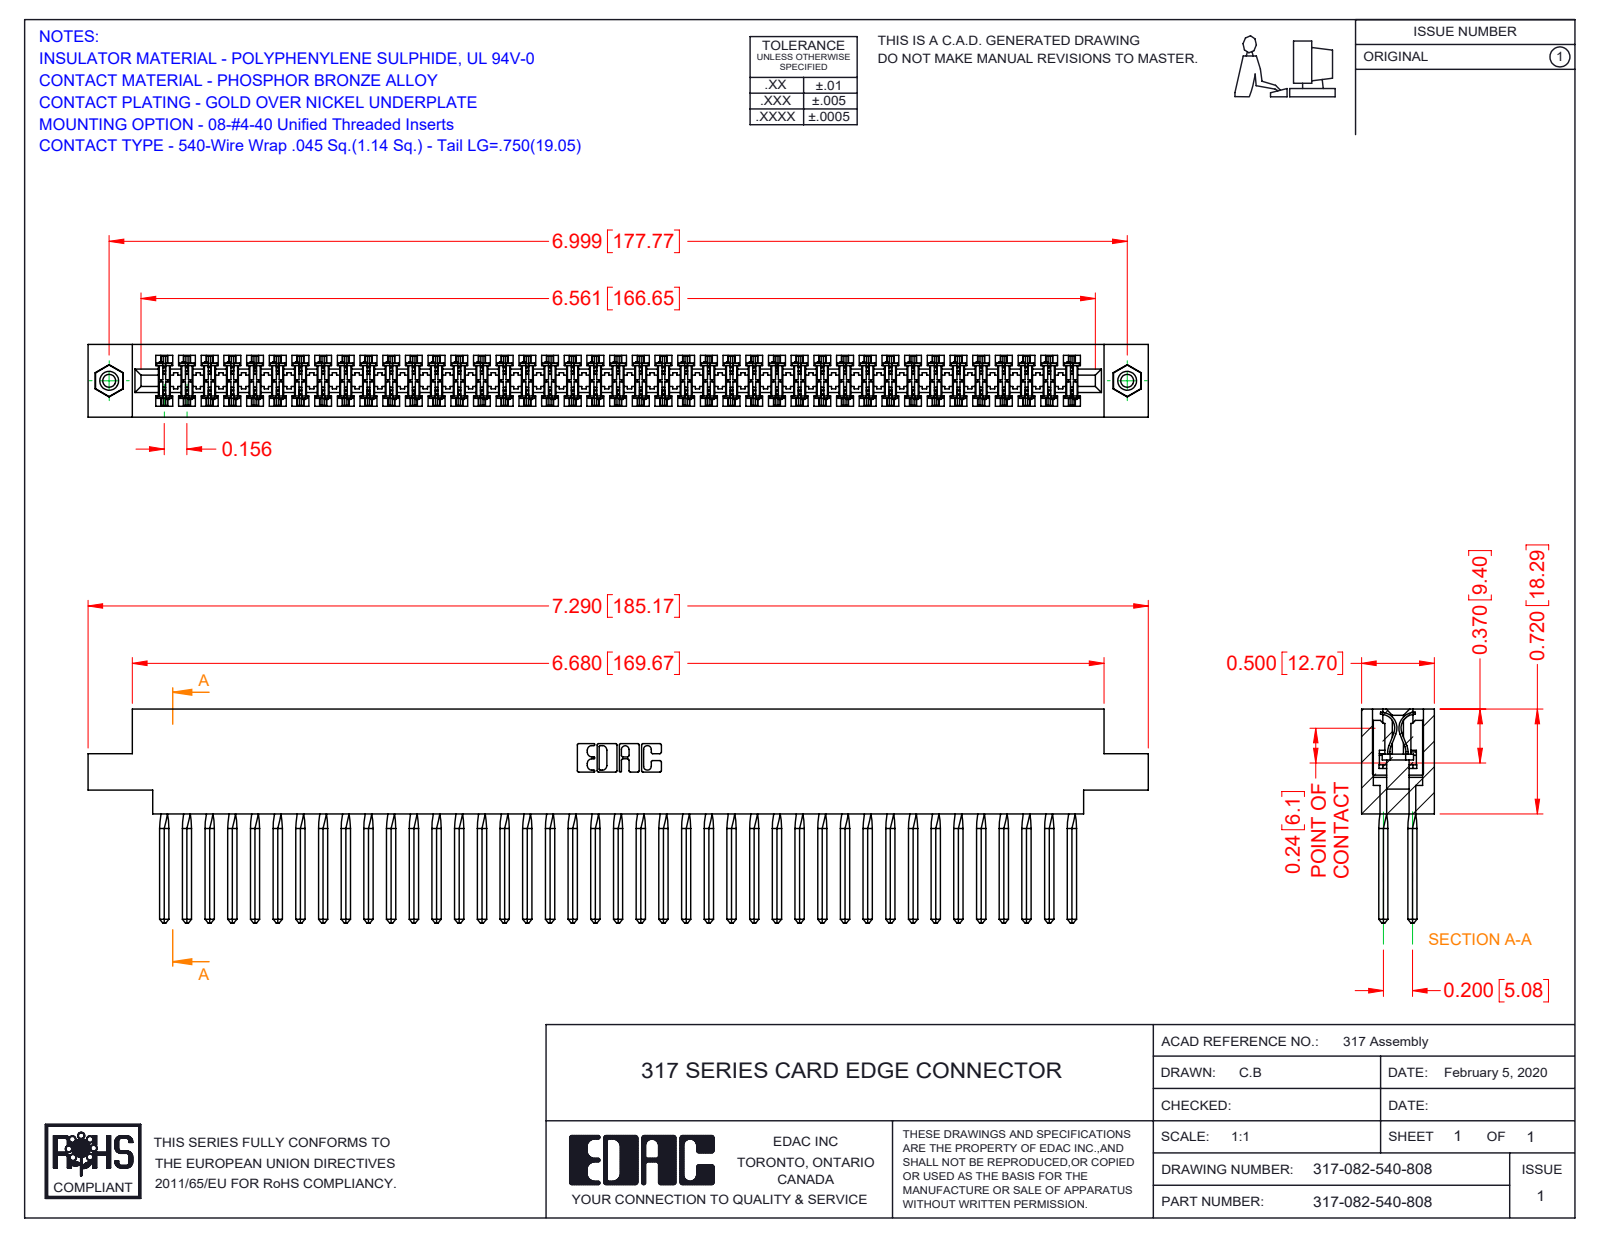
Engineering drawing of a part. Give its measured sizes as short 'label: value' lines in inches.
name: 317 Part_.156 Dia - TI; 317-290-001_540; 345-250-001_345-250-003-102; 317-082-540-878
written by: SolidWorks 2016 (CONFIG_CONTROL_DESIGN)
unit: in
bodies: 85 solids, 7460 faces (6076 planar, 1040 cylindrical, 344 other)
size: 7.29 × 1.47 × 0.5
volume: 1.894 in³; area: 71.7 in²
holes: 2× ⌀0.089, 2× ⌀0.125, 2× ⌀0.156
bosses: 2× ⌀0.155
rounds: 164× R0.015, 22× R0.01, 6× R0.007, 6× R0.031, 3× R0.026, 2× R0.095, 2× R0.1, 2× R0.11
face distances: 0.5, 0.075, 0.425, 0.35, 0.195, 0.094, 0.2, 0.115, 0.131, 0.046
hole spacings: 6.999
